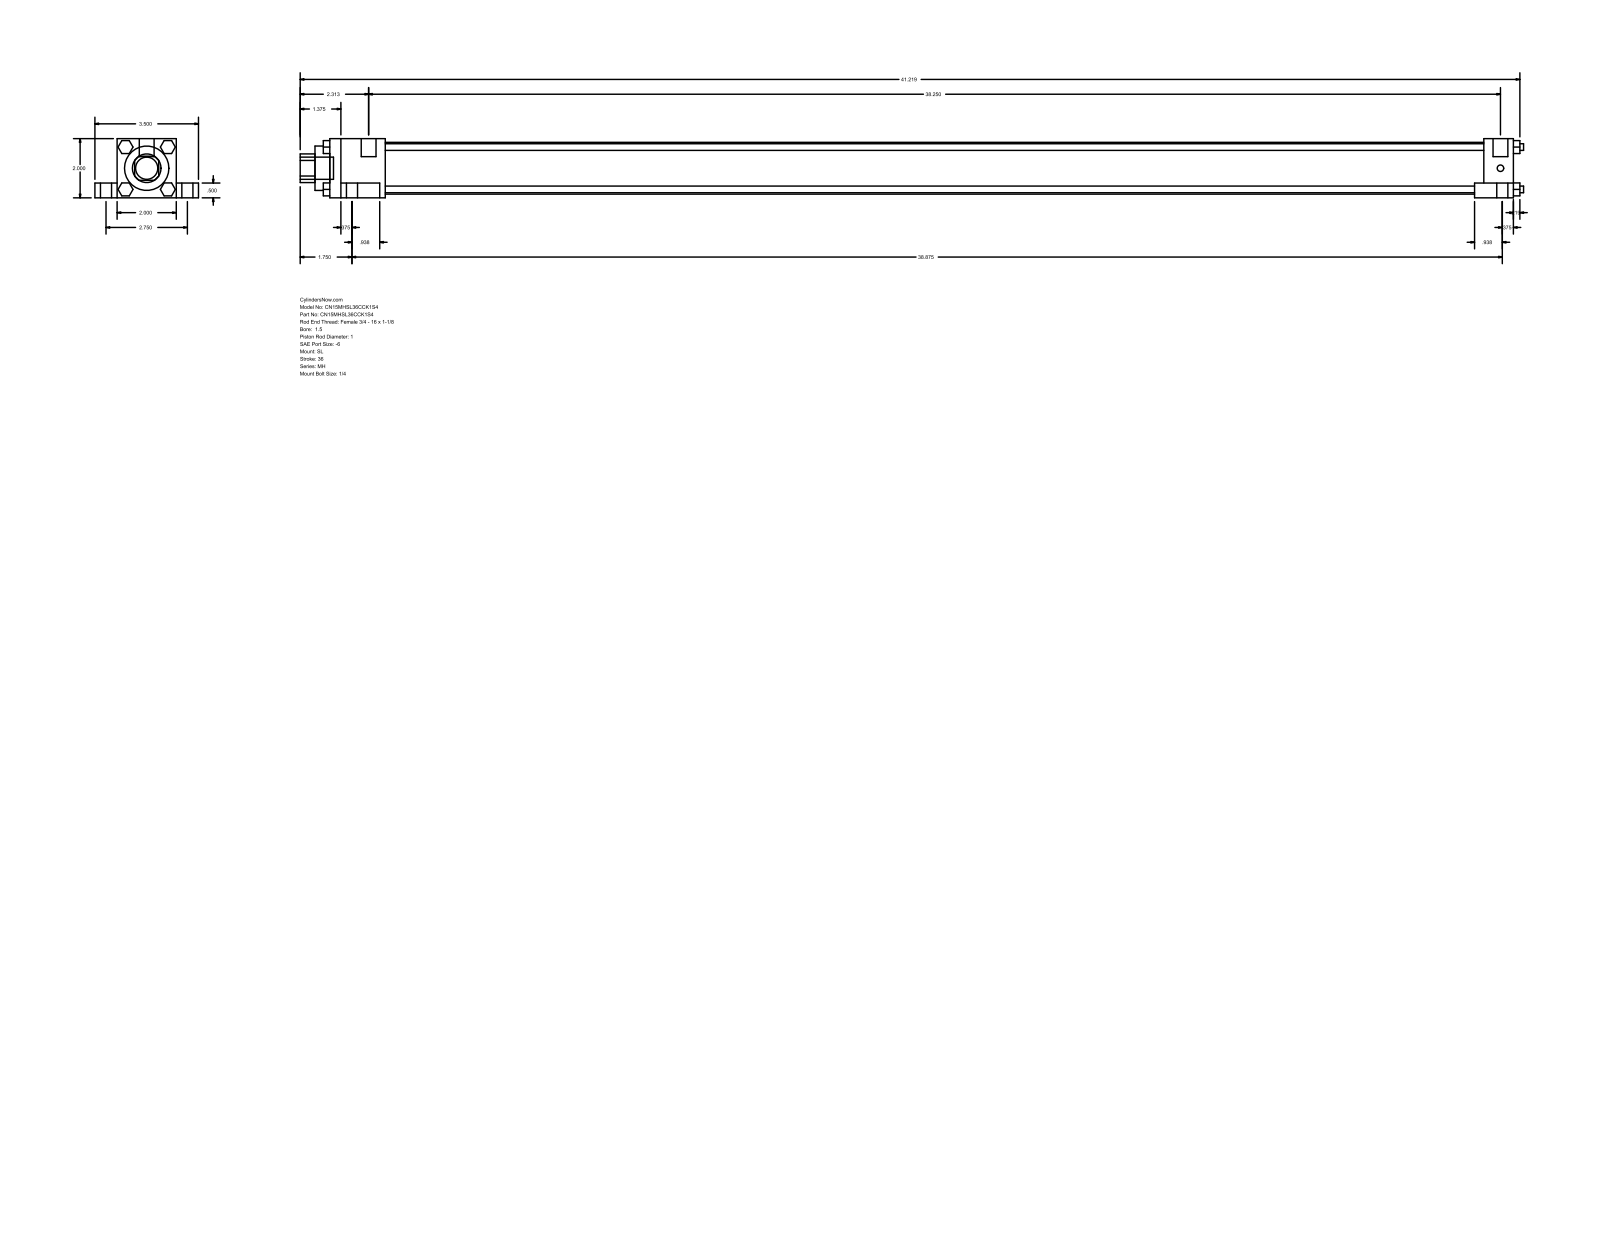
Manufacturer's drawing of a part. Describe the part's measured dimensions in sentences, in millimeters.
The part is named "MH_SL__0150_1". Its 3-D file was written by "GSSL Pune (CONFIG_CONTROL_DESIGN)". It is 0 solids with 148 faces: 112 planar, 36 cylindrical and 0 other. Overall it measures 1050.13 by 88.9 by 50.8 millimeters. Round holes: 1 of diameter 25.4, 1 of diameter 38.1, 1 of diameter 44.45. Round bosses or shafts: 4 of diameter 15.88, 4 of diameter 9.53, 4 of diameter 5.71, 4 of diameter 5.56, 2 of diameter 12.7, 1 of diameter 19.05. Partial cylindrical surfaces (rounded edges, fillets, slot ends): 1 of radius 12.29. The main face-to-face distances are 50.8, 12.7, 38.1, 19.05, 69.85, 1016, 25.4, 9.52, 33.34, 973.14.
